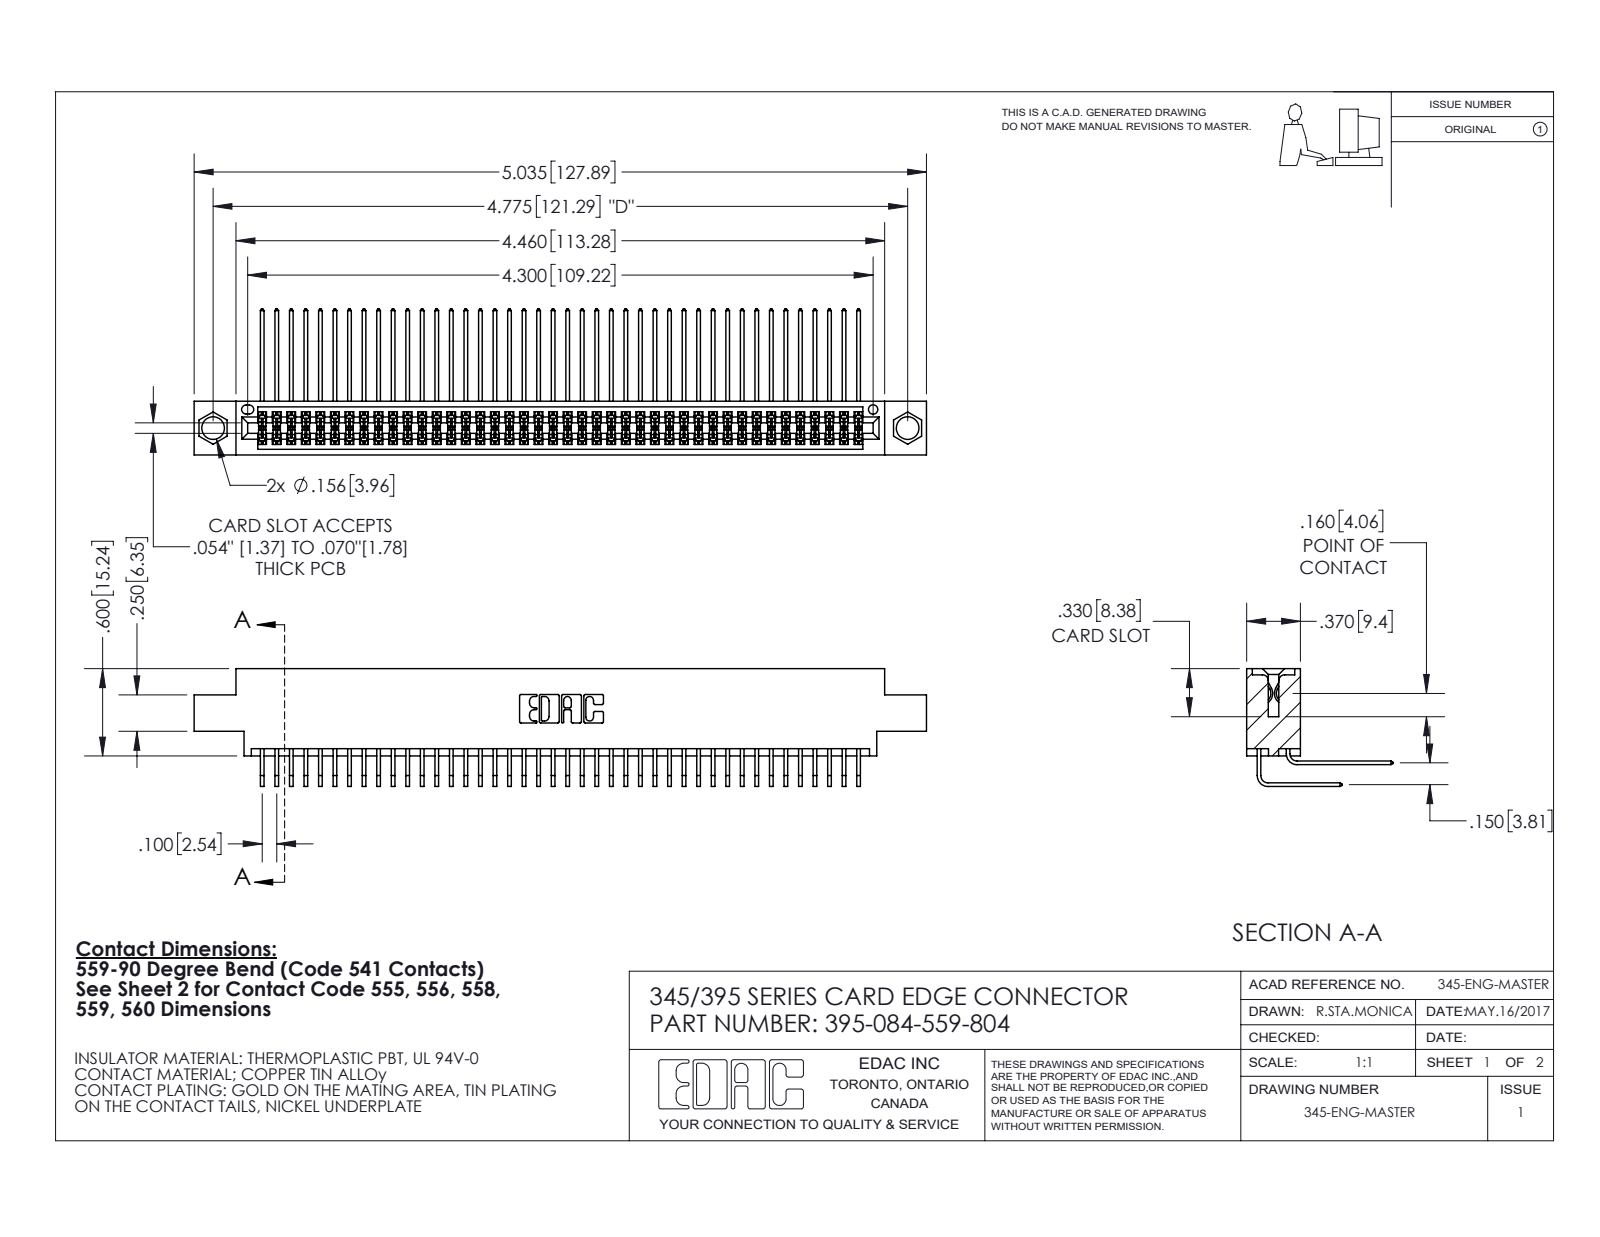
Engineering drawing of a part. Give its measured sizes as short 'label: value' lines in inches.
name: 395-084-559-804; 345-292-001_559 Tail - 2; 345-292-001_558 559 Tail - 1; 345 Part_0.170 Offset - 0.156 Dia-TI
written by: SolidWorks 2020 (CONFIG_CONTROL_DESIGN)
unit: in
bodies: 85 solids, 4512 faces (3038 planar, 1474 cylindrical, 0 other)
size: 5.035 × 1.005 × 0.809
volume: 0.774 in³; area: 32.6 in²
holes: 2× ⌀0.156, 1× ⌀0.064
rounds: 168× R0.006, 22× R0.01, 6× R0.007, 6× R0.031, 3× R0.026, 2× R0.014, 2× R0.019, 2× R0.022
face distances: 0.072, 0.298, 0.2, 0.37, 0.098, 0.272, 0.025, 0.225, 0.175, 0.15
hole spacings: 0.27, 4.539, 4.775
